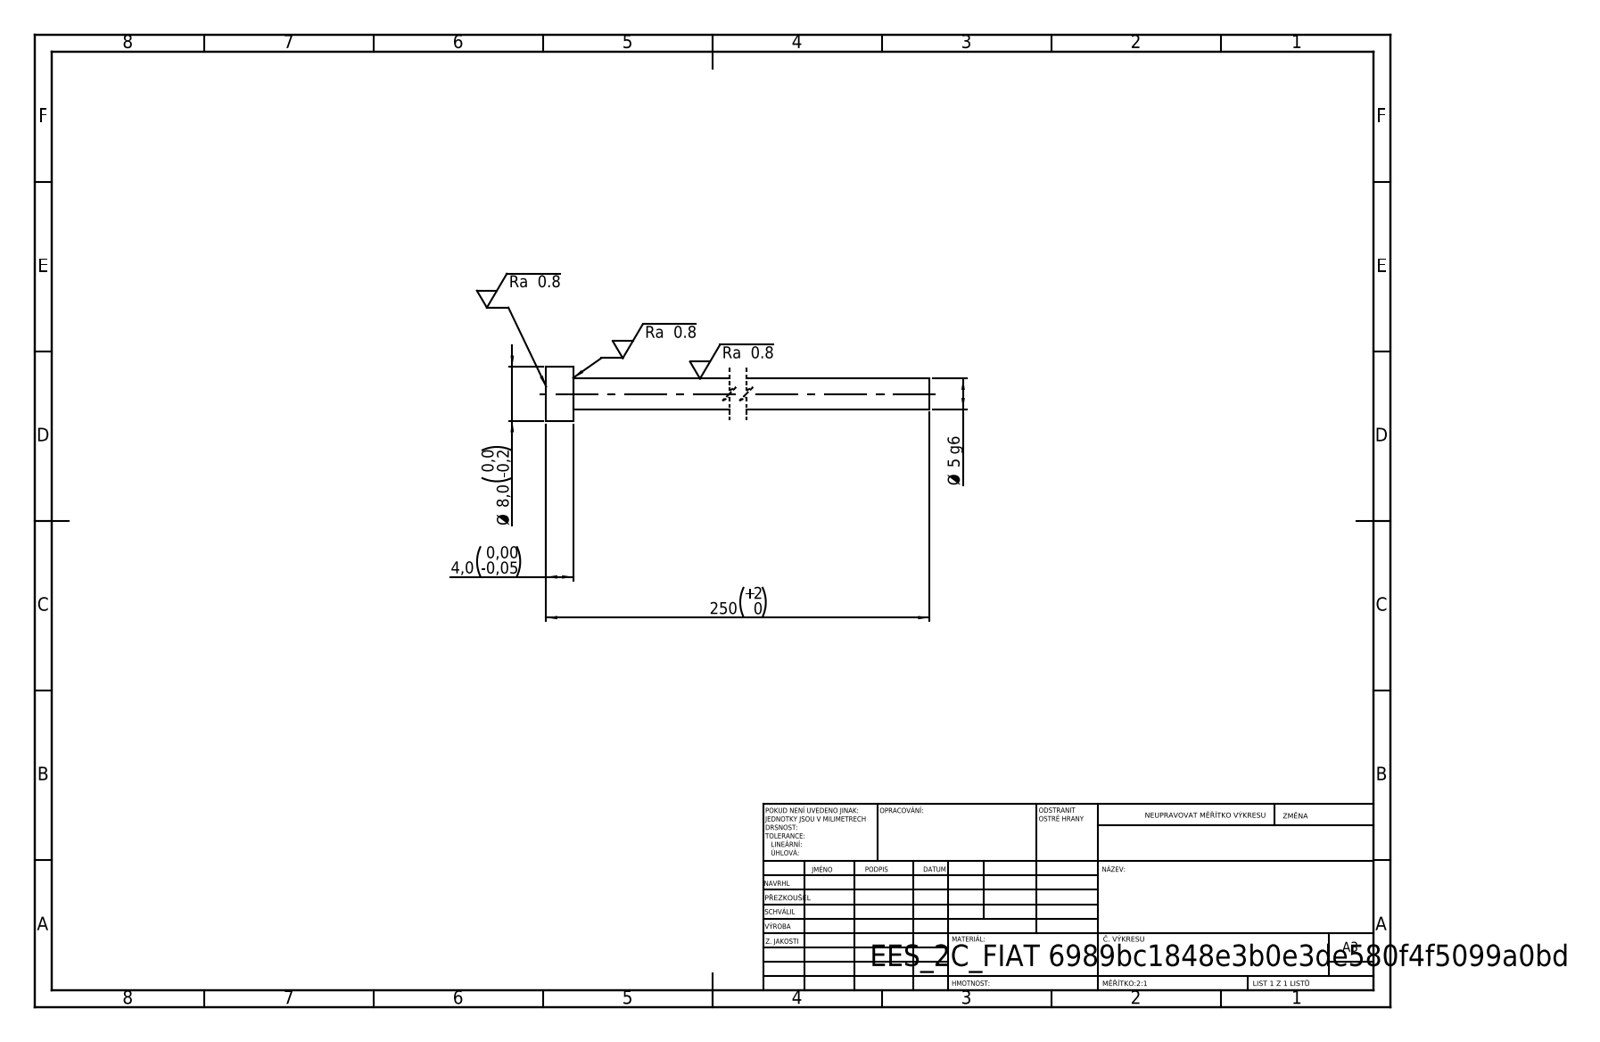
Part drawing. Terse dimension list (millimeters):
written by: SolidWorks 2019 (CONFIG_CONTROL_DESIGN)
unit: mm
bodies: 1 solid, 7 faces (3 planar, 4 cylindrical, 0 other)
size: 250 × 8 × 8
volume: 4 114 mm³; area: 3 679 mm²
bosses: 1× ⌀8, 1× ⌀4.5
face distances: 4, 250, 246
